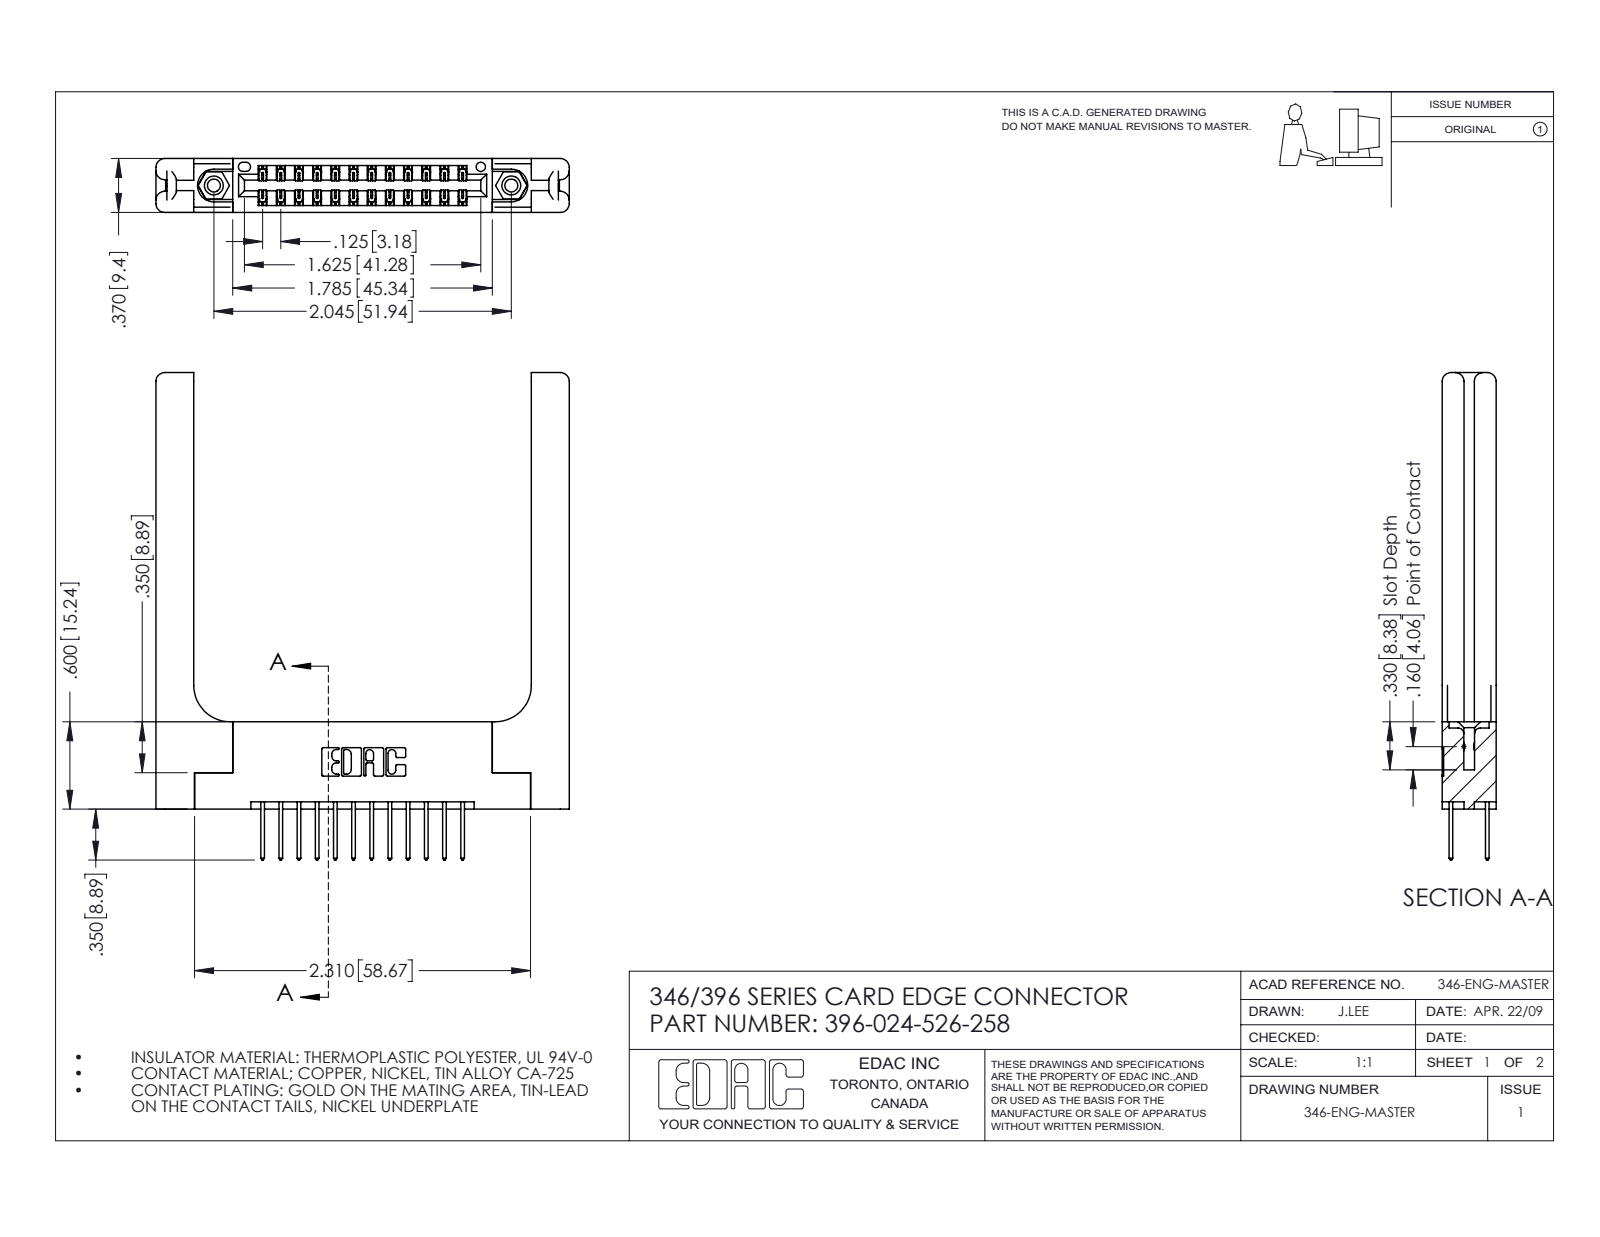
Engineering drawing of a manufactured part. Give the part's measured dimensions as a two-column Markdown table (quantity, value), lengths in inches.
| quantity | value |
| --- | --- |
| part name | 345-250-001_345-250-001-102; 346 Part_Flush Mounting Lugs - 0.156 Dia-TH; 346-220-058_345-220-058; 345-292-001_345-293-126 (+1 more) |
| STEP written by | SolidWorks 2016 (CONFIG_CONTROL_DESIGN) |
| units | inches |
| bodies | 29 solids, 1626 faces (1064 planar, 502 cylindrical, 60 other) |
| overall size | 3.35 × 2.841 × 0.37 |
| volume | 0.875 in³ |
| surface area | 21.83 in² |
| round holes (diameter × count) | 0.089 × 2, 0.125 × 2, 0.156 × 2, 0.064 × 1 |
| round bosses / shafts (diameter × count) | 0.155 × 2 |
| partial cylindrical surfaces (radius × count) | 0.006 × 36, 0.01 × 24, 0.01 × 22, 0.06 × 16, 0.007 × 6, 0.031 × 6, 0.026 × 3, 0.014 × 2 |
| main face-to-face distances | 0.37, 0.15, 0.072, 0.148, 0.048, 0.322, 0.25, 0.102, 0.22, 0.173 |
| hole center spacings | 0.246, 1.839, 2.045 |
